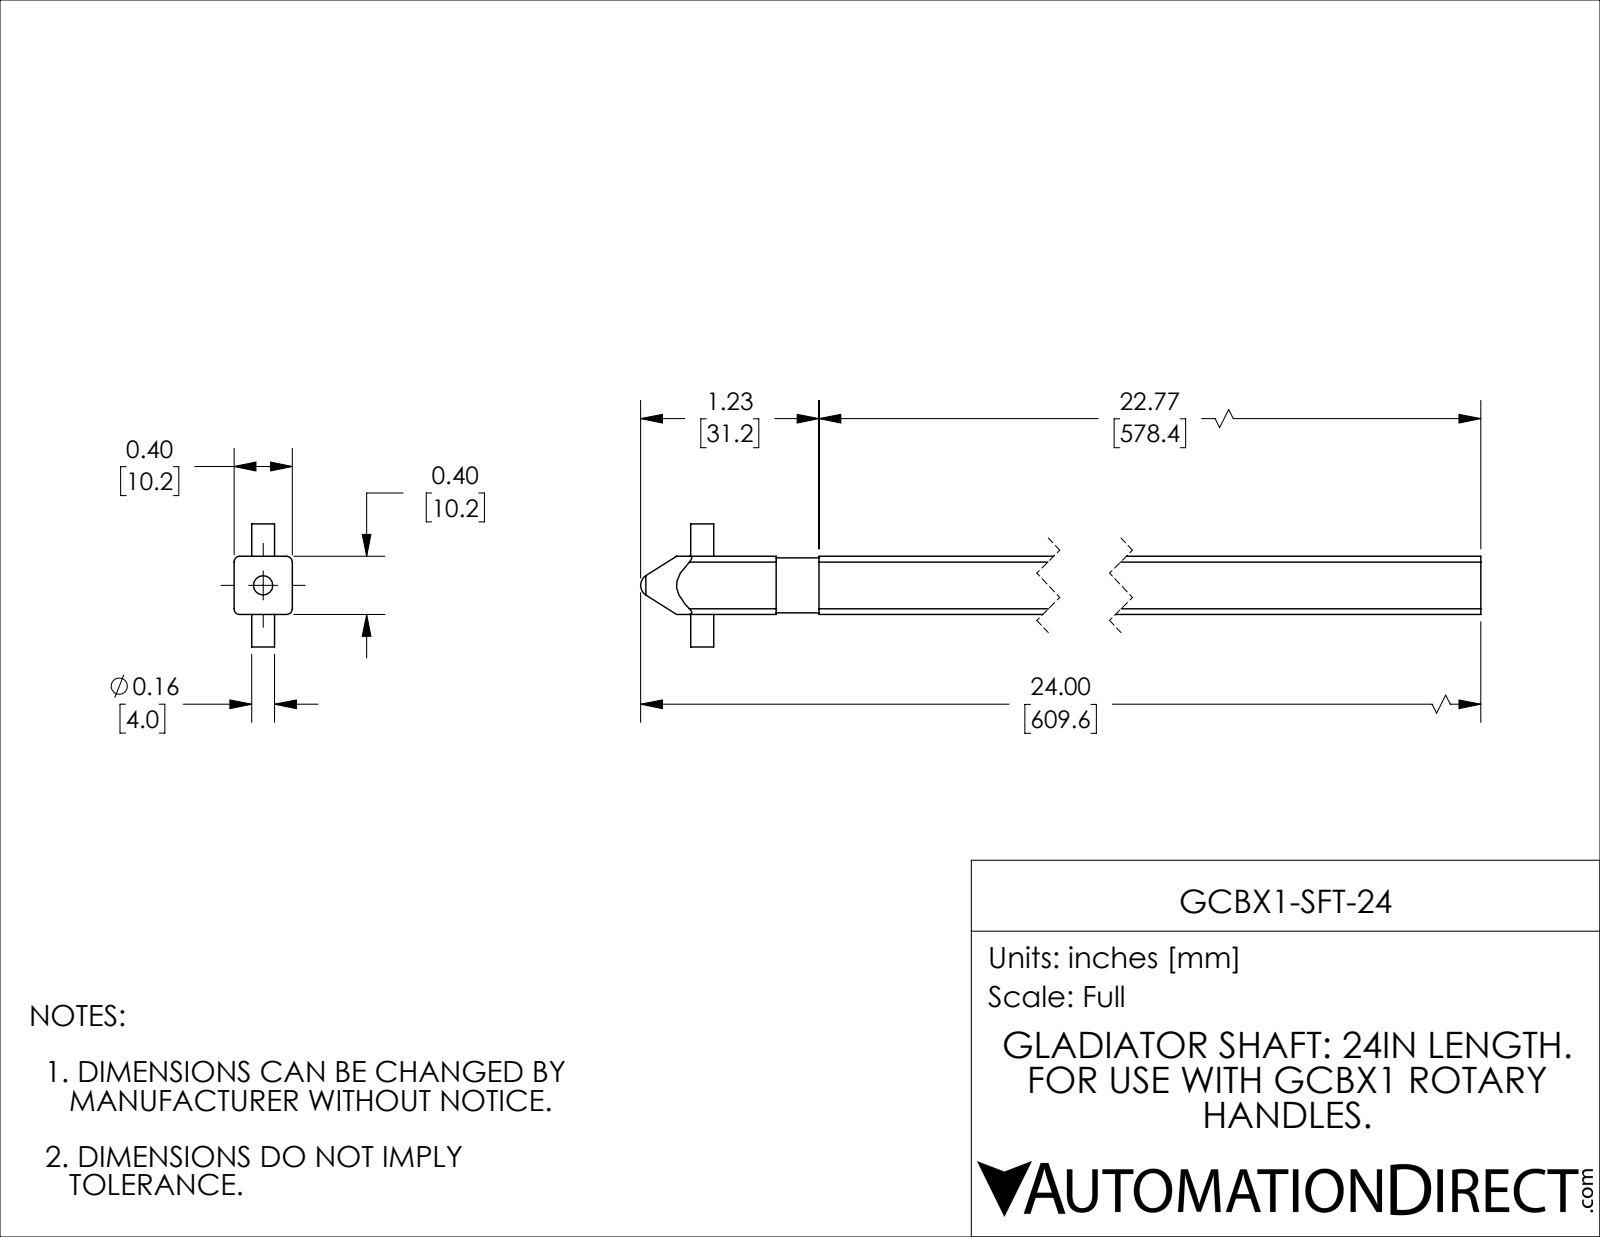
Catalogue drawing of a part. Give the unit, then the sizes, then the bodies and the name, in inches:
Units: inches
Overall size (bounding box): 23.999 × 0.846 × 0.4
Round holes (diameter × count): ⌀0.142 ×1
Round bosses / shafts (diameter × count): ⌀0.378 ×1, ⌀0.157 ×1
Partial cylindrical surfaces — rounded edges, fillets, slot ends (radius × count): R0.039 ×4
Main face-to-face distances: 0.4, 22.773, 23.068, 0.295, 0.194, 0.206, 0.223, 0.623, 0.846
Volume: 3.764 in³ · Surface area: 37.72 in²
Bodies: 2 solids, 37 faces (17 planar, 17 cylindrical, 3 other)
Part name (STEP PRODUCT): GCBX1-SFT-24
STEP written by: SolidWorks 2021 (CONFIG_CONTROL_DESIGN)
